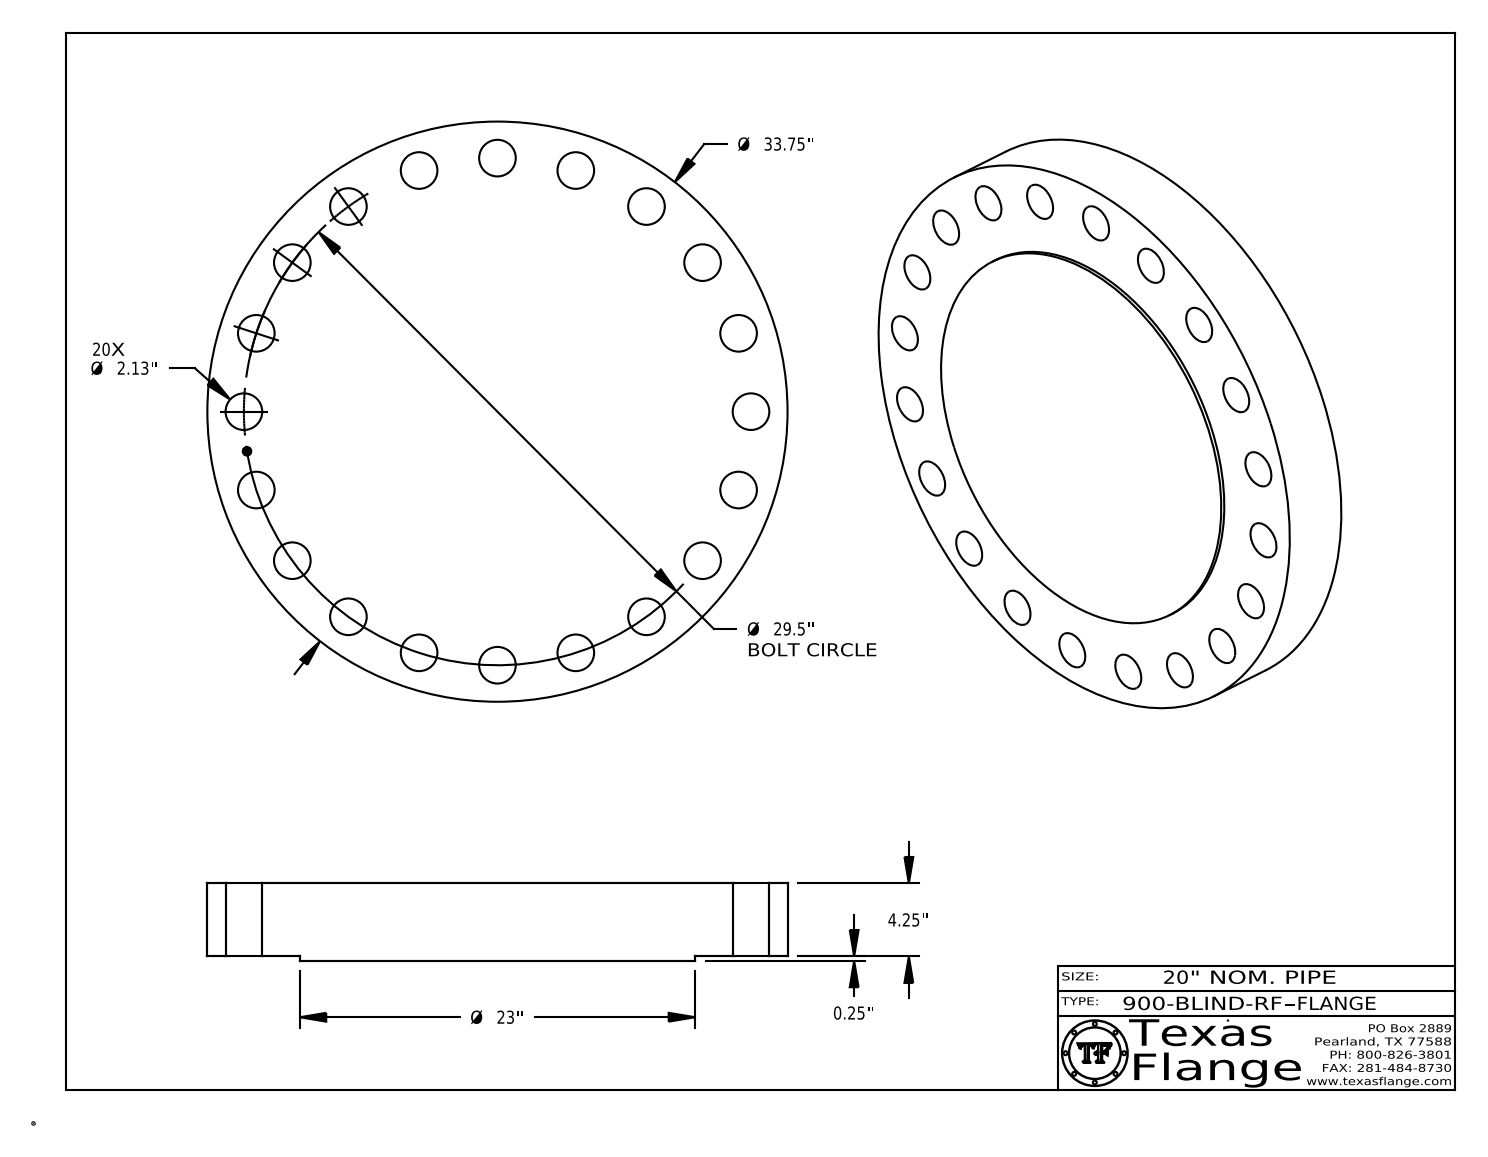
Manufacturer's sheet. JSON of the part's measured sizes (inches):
{"part_name": "900-BLIND-RF", "step_written_by": "CATIA V5 STEP AP214 (AUTOMOTIVE_DESIGN)", "units": "inches", "bodies": {"solids": 1, "faces": 432, "planar": 368, "cylindrical": 64, "other": 0}, "overall_size": [33.75, 33.75, 4.5], "volume_in3": 3603, "surface_area_in2": 2684, "round_holes": [[2.13, 20], [0.495, 1]], "round_bosses_or_shafts": [[0.03, 8], [33.75, 1], [23, 1], [0.39, 1]], "face_to_face_distances": [4.5, 0.25, 4.25, 4.485, 4.235, 0.015, 0.148, 0.145, 0.027, 0.096], "hole_center_spacings": [29.137, 4.615, 17.34, 20.859, 23.866, 26.285, 9.116, 13.393]}
